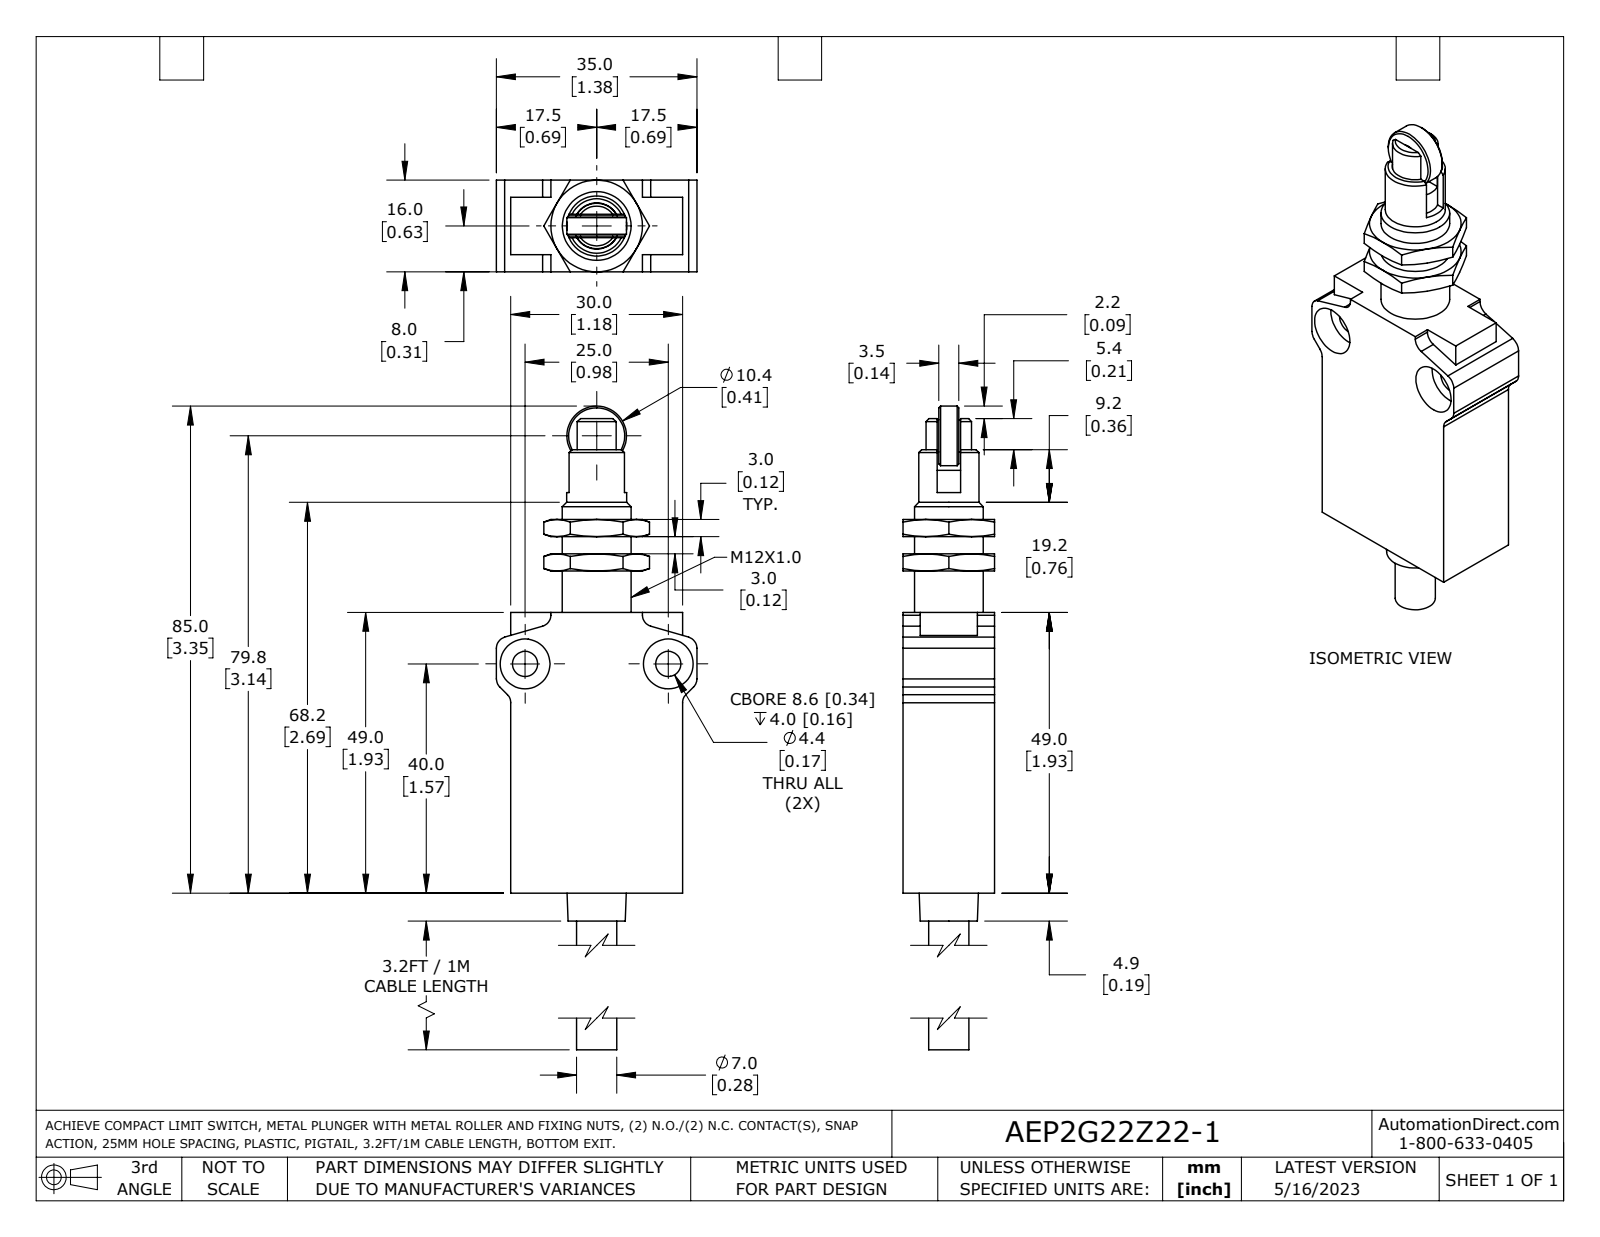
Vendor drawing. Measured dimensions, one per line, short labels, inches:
name: AEP2G22Z22-1
written by: SolidWorks 2021 (AUTOMOTIVE_DESIGN)
unit: in
bodies: 3 solids, 141 faces (74 planar, 31 cylindrical, 36 other)
size: 3.933 × 1.378 × 0.63
volume: 1.655 in³; area: 16.13 in²
holes: 2× ⌀0.173, 2× ⌀0.343, 1× ⌀0.317, 1× ⌀0.472
bosses: 1× ⌀0.413, 1× ⌀0.409, 1× ⌀0.313, 1× ⌀0.276, 1× ⌀0.22
rounds: 8× R0.079, 1× R0.256
face distances: 0.63, 1.181, 0.118, 1.929, 0.472, 0.236, 0.354, 0.157, 0.098, 1.28
hole spacings: 0.984
